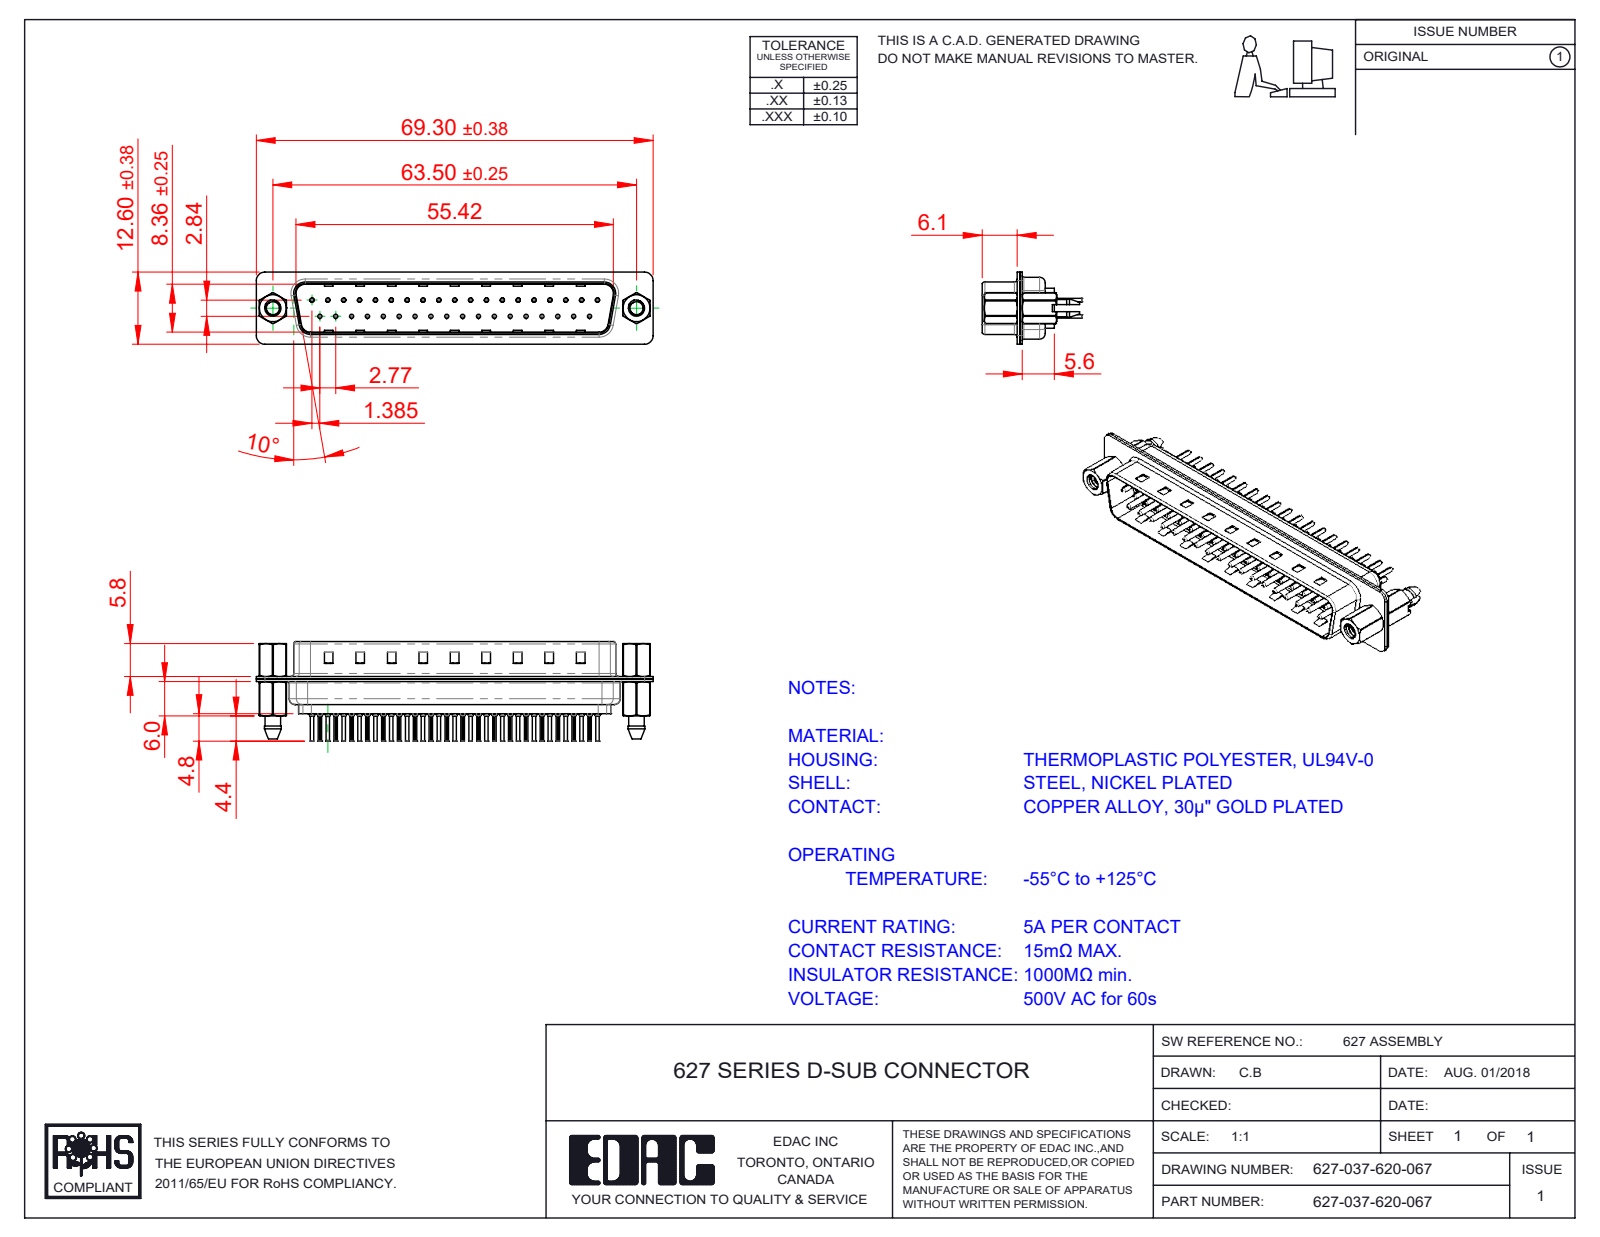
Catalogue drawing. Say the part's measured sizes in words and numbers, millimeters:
The part is named "627 Contact Row 1_20L; 627 Contact Row 2_20L; 627 Shell Front_37 Contacts; 627 Housing_37 LP (+4 more)". Its 3-D file was written by "SolidWorks 2020 (CONFIG_CONTROL_DESIGN)". It is 44 solids with 4238 faces: 1145 planar, 1614 cylindrical and 1479 other. Overall it measures 69.3 by 17.3 by 12.6 millimeters. Its volume is 4 028 cubic millimeters and its surface area 11 455 square millimeters. Round holes: 37 of diameter 0.2, 37 of diameter 0.35, 37 of diameter 1.1, 37 of diameter 1.6, 2 of diameter 2.26, 2 of diameter 2.29, 2 of diameter 4, 2 of diameter 4.8. Round bosses or shafts: 37 of diameter 2, 37 of diameter 1.5, 37 of diameter 0.75, 37 of diameter 0.6, 2 of diameter 4.9, 2 of diameter 2.79. Partial cylindrical surfaces (rounded edges, fillets, slot ends): 74 of radius 0.1, 18 of radius 1.5, 12 of radius 2, 10 of radius 1.6, 8 of radius 0.5, 4 of radius 0.25, 4 of radius 0.6, 4 of radius 0.65. The main face-to-face distances are 0.4, 0.82, 9.58, 0.45, 8.76, 1.5, 0.9, 1.4, 6.5, 6.05. The hole center spacings are 3.16, 2.77, 5.54, 8.31, 5.04, 10.1, 11.08, 12.78.
